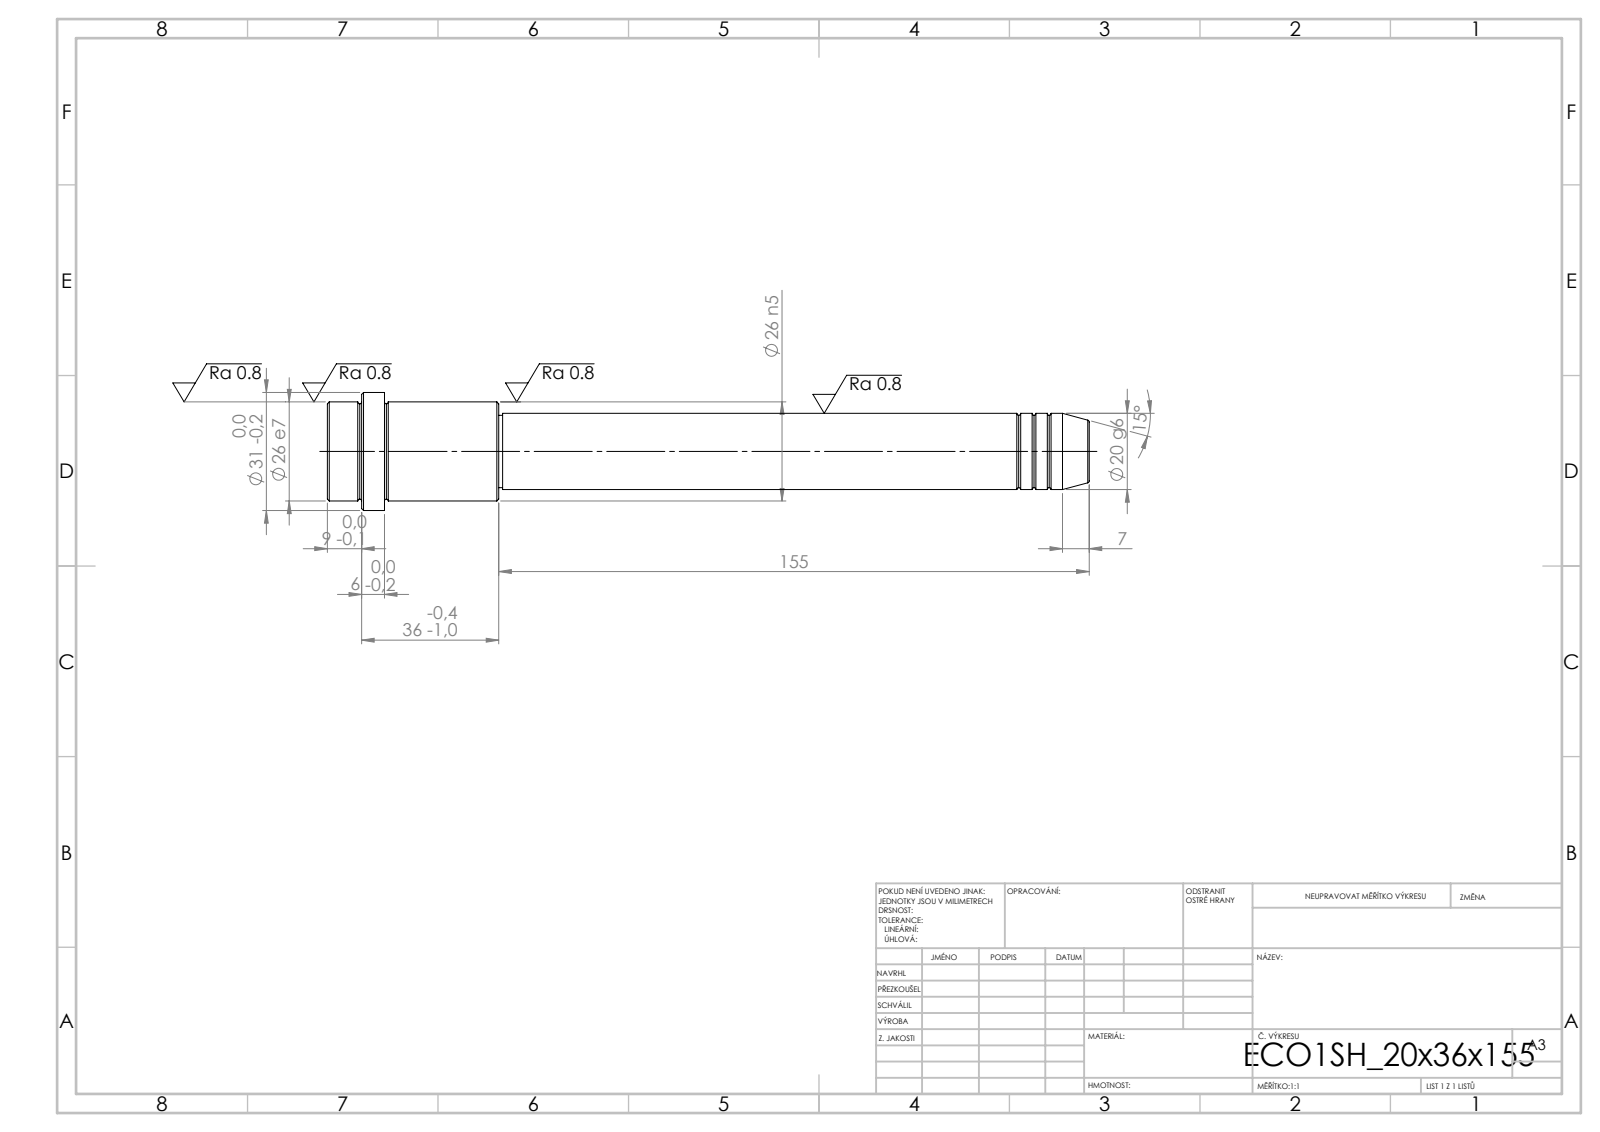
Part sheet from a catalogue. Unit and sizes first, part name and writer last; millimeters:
Units: millimetres
Overall size (bounding box): 200 × 31 × 31
Round bosses / shafts (diameter × count): ⌀31 ×1, ⌀26 ×1, ⌀20 ×1, ⌀19 ×1
Main face-to-face distances: 15, 30, 45, 155, 185, 200, 191, 36, 6, 9
Volume: 73 343 mm³ · Surface area: 15 044 mm²
Bodies: 1 solid, 52 faces (6 planar, 16 cylindrical, 30 other)
STEP written by: SolidWorks 2019 (CONFIG_CONTROL_DESIGN)
